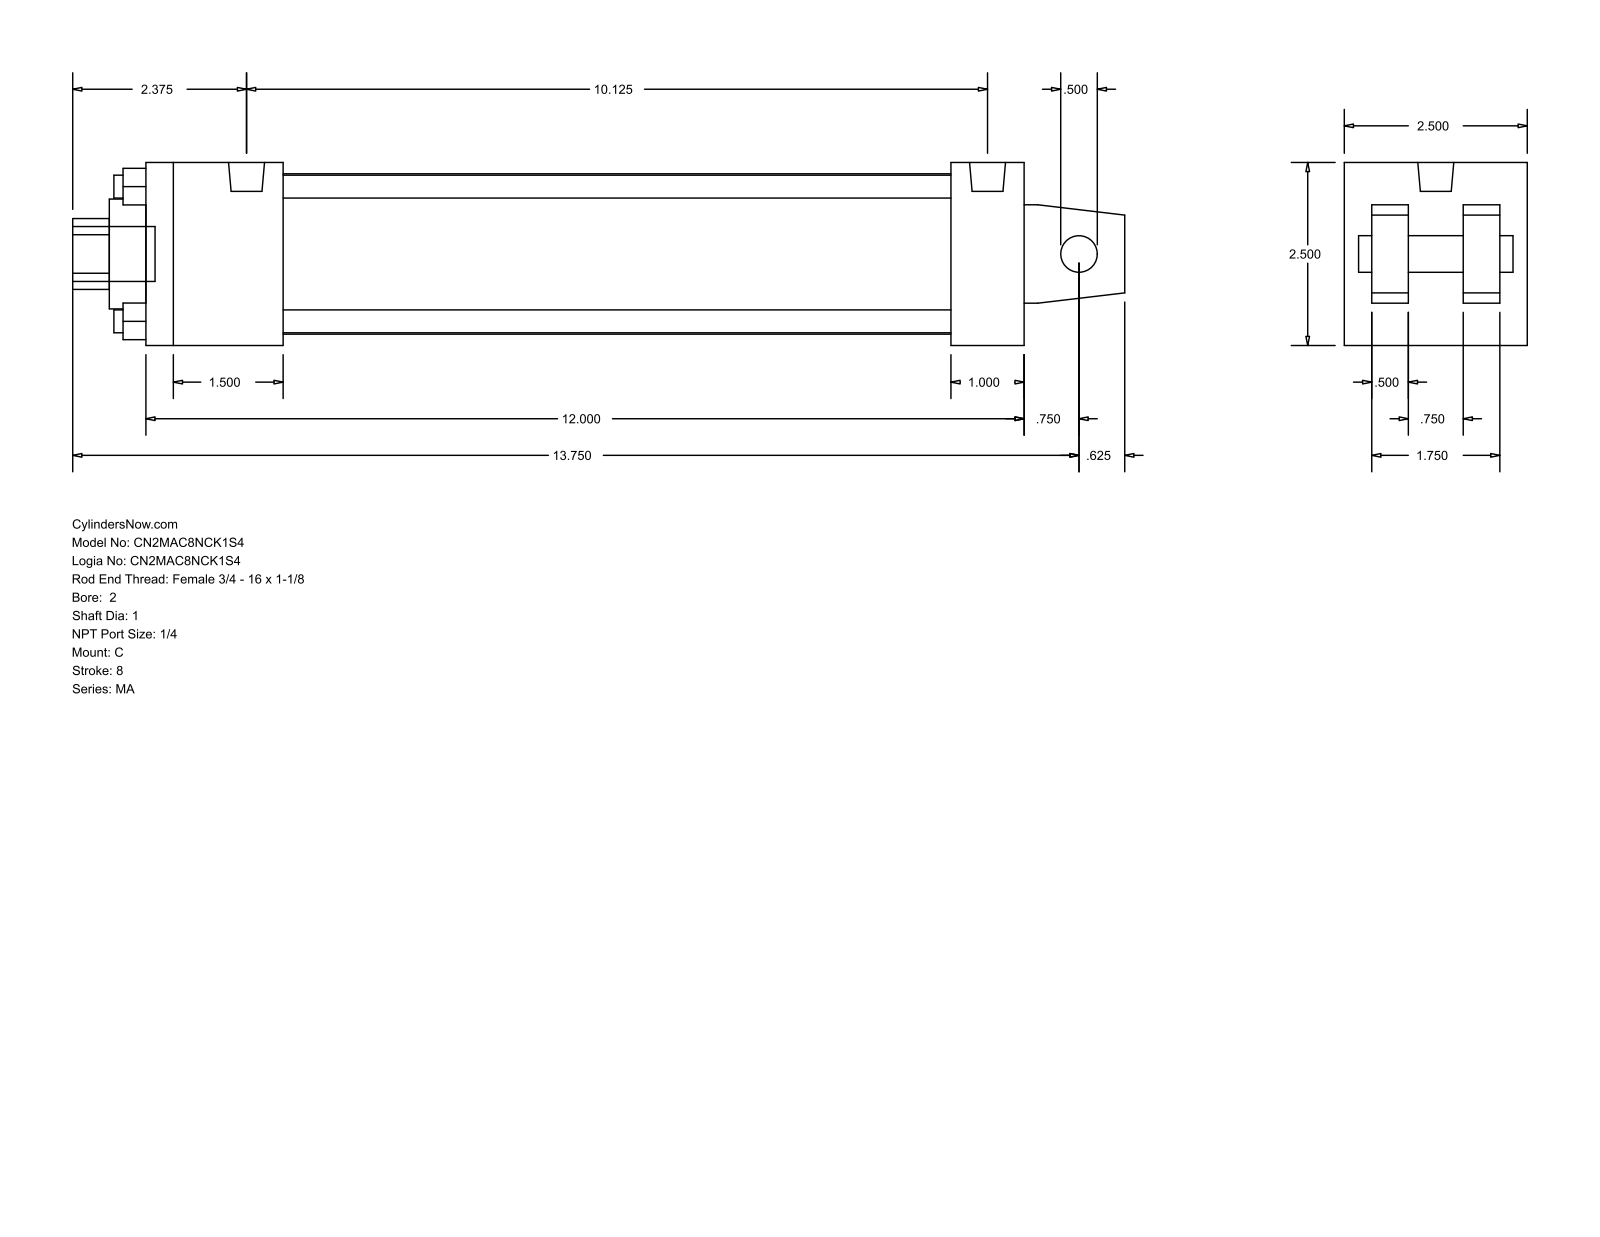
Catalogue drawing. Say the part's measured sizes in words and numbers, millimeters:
The part is named "MA_C__0200_1". Its 3-D file was written by "GSSL Pune (CONFIG_CONTROL_DESIGN)". It is 0 solids with 103 faces: 76 planar, 27 cylindrical and 0 other. Overall it measures 365.12 by 63.5 by 63.5 millimeters. Round holes: 4 of diameter 7.94, 1 of diameter 12.7, 1 of diameter 25.4, 1 of diameter 38.1, 1 of diameter 55.63. Round bosses or shafts: 4 of diameter 7.94, 2 of diameter 12.49, 1 of diameter 19.05. Partial cylindrical surfaces (rounded edges, fillets, slot ends): 1 of radius 12.29. The main face-to-face distances are 63.5, 12.7, 304.8, 22.22, 41.28, 9.52, 53.98, 31.76, 47.63, 25.4. The hole center spacings are 33.05, 46.74, 66.1.
